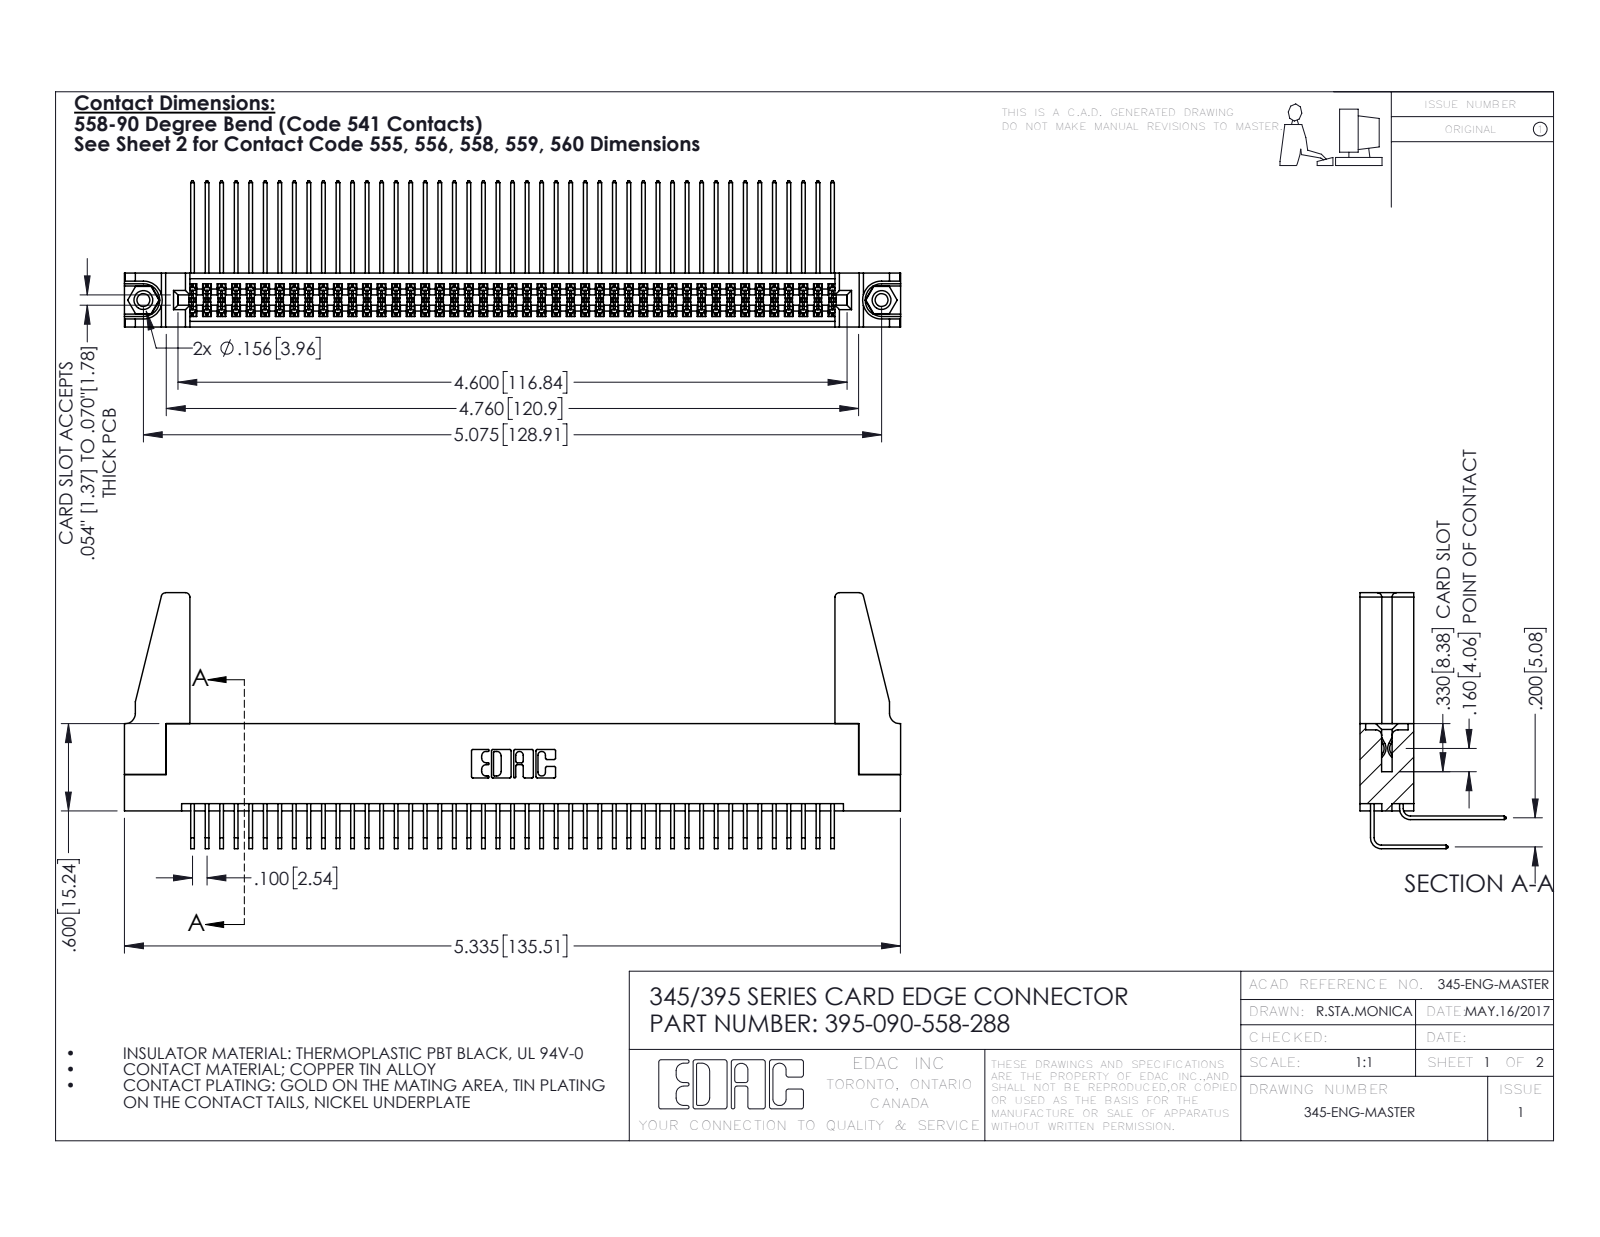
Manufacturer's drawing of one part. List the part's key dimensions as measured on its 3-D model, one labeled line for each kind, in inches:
Part name (STEP PRODUCT): 345-292-001_558 Tail - 2; 345-292-001_558 559 Tail - 1; 345-220-078_345-220-088; 345 Part_Flush Mounting Lugs - 0.156 Dia-TH (+2 more)
STEP written by: SolidWorks 2016 (CONFIG_CONTROL_DESIGN)
Units: inches
Bodies: 95 solids, 4930 faces (3302 planar, 1612 cylindrical, 16 other)
Overall size (bounding box): 5.336 × 1.759 × 1.005
Volume: 1.035 in³ · Surface area: 40.13 in²
Round holes (diameter × count): ⌀0.089 ×2, ⌀0.125 ×2, ⌀0.156 ×2, ⌀0.064 ×1
Round bosses / shafts (diameter × count): ⌀0.155 ×2
Partial cylindrical surfaces — rounded edges, fillets, slot ends (radius × count): R0.006 ×136, R0.01 ×22, R0.03 ×8, R0.007 ×6, R0.031 ×6, R0.026 ×3, R0.014 ×2, R0.019 ×2
Main face-to-face distances: 0.072, 0.298, 0.2, 0.37, 0.098, 0.272, 0.025, 0.225, 0.285, 0.025
Hole centre spacings: 0.27, 4.839, 5.075
